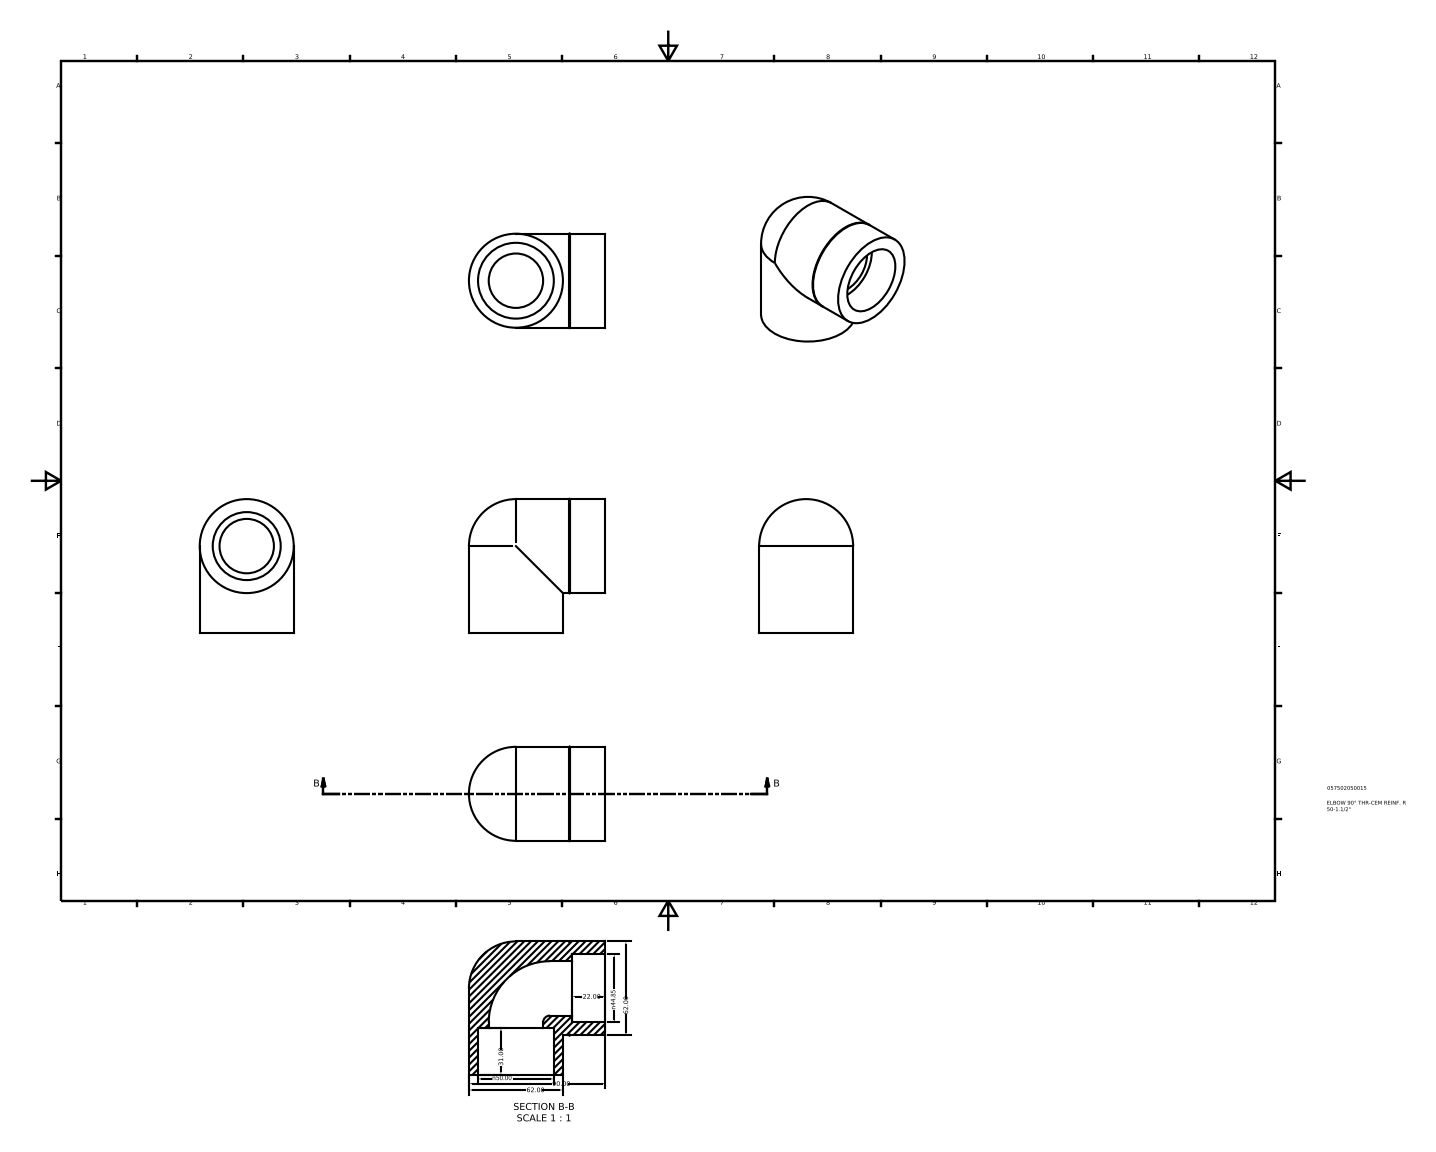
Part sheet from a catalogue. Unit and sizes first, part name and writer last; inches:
Units: inches
Overall size (bounding box): 3.543 × 3.465 × 2.441
Round holes (diameter × count): ⌀1.413 ×2, ⌀1.765 ×1, ⌀1.969 ×1
Round bosses / shafts (diameter × count): ⌀2.441 ×2
Main face-to-face distances: 1.22, 0.866
Volume: 11.72 in³ · Surface area: 61.83 in²
Bodies: 1 solid, 15 faces (4 planar, 7 cylindrical, 4 other)
Part name (STEP PRODUCT): 057502050015
STEP written by: Autodesk Inventor 2015 (AUTOMOTIVE_DESIGN)
